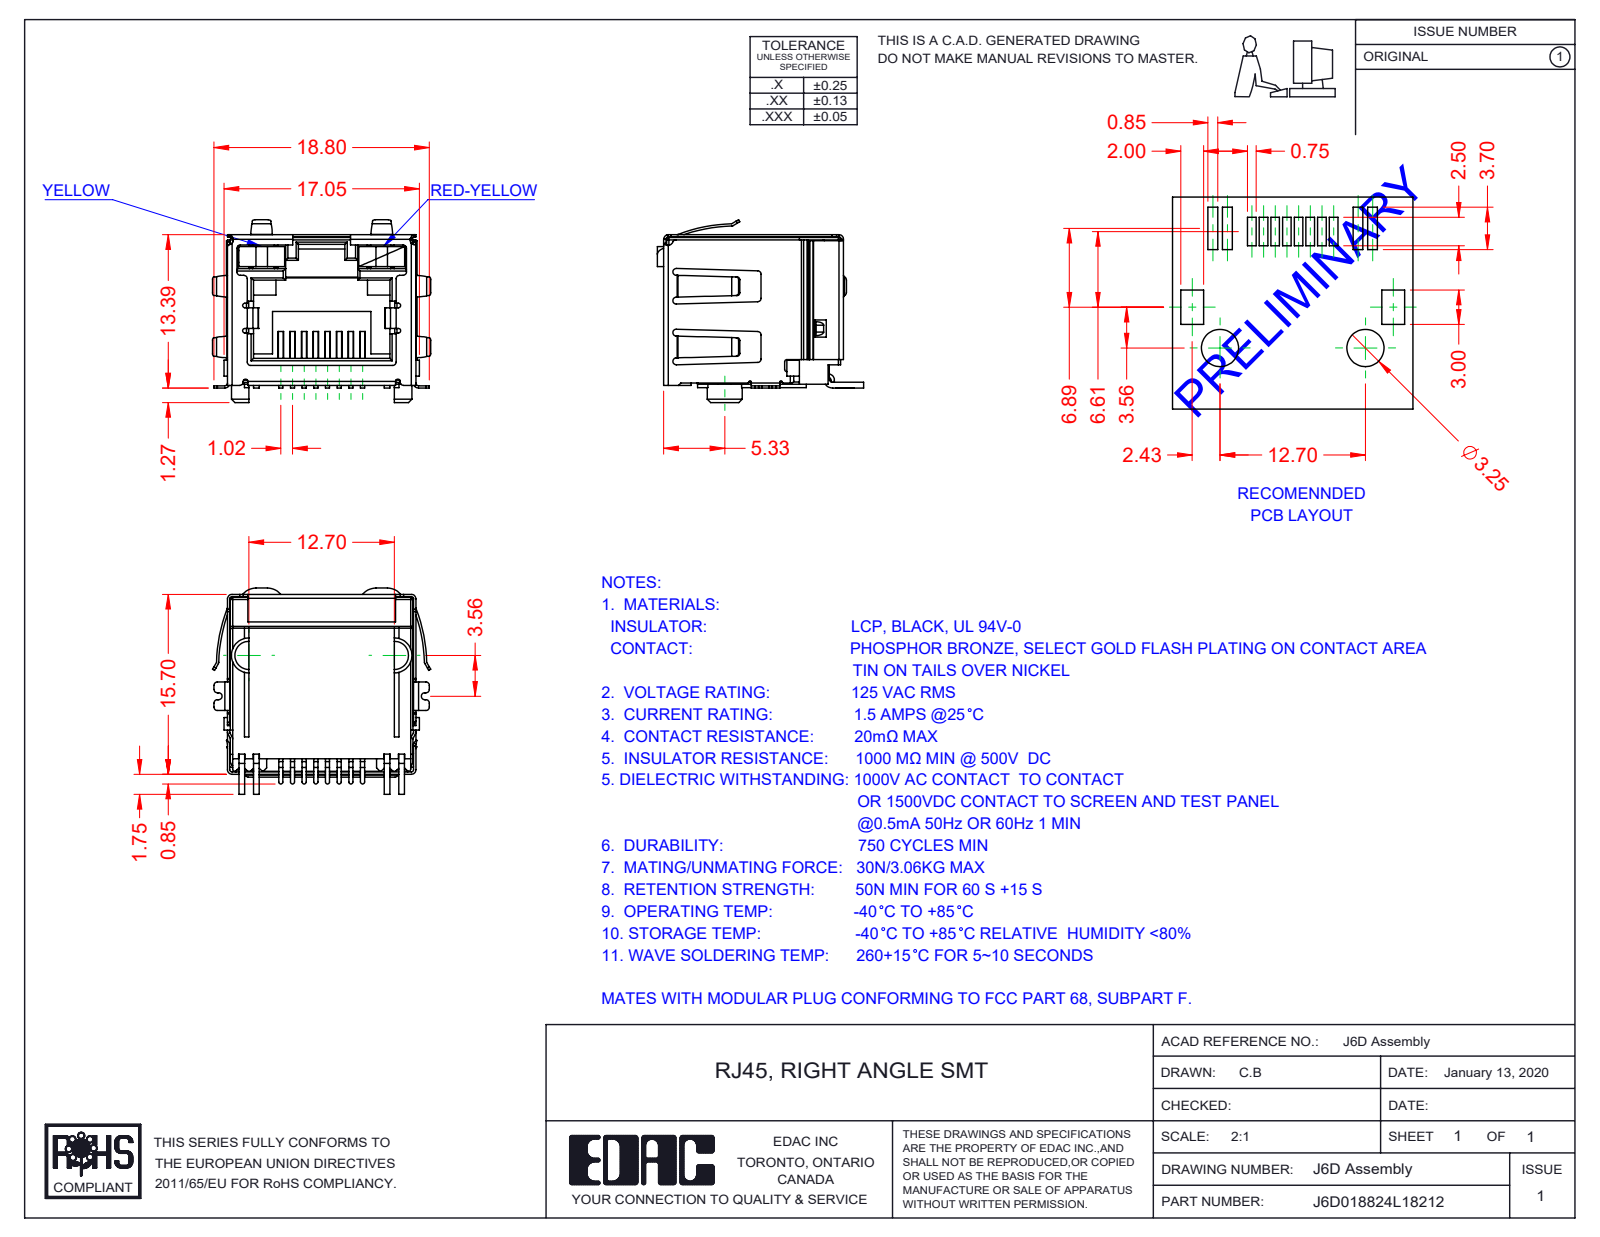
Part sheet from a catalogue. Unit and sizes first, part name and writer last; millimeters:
Units: millimetres
Overall size (bounding box): 19.06 × 18 × 15.95
Partial cylindrical surfaces — rounded edges, fillets, slot ends (radius × count): R0.3 ×55, R0.2 ×40, R0.4 ×19, R0.25 ×16, R0.1 ×12, R0.15 ×8, R0.18 ×8, R0.5 ×6
Main face-to-face distances: 16, 16.2, 16.25, 2.25, 1, 15.95, 12.8, 0.45, 13.05, 10.6
Volume: 1 790 mm³ · Surface area: 4 796 mm²
Bodies: 12 solids, 1031 faces (702 planar, 284 cylindrical, 45 other)
Part name (STEP PRODUCT): 6D Shield_LED - EMI; 6D Insulator; J6D018824L18212; 6D Contacts (+2 more)
STEP written by: SolidWorks 2016 (CONFIG_CONTROL_DESIGN)
